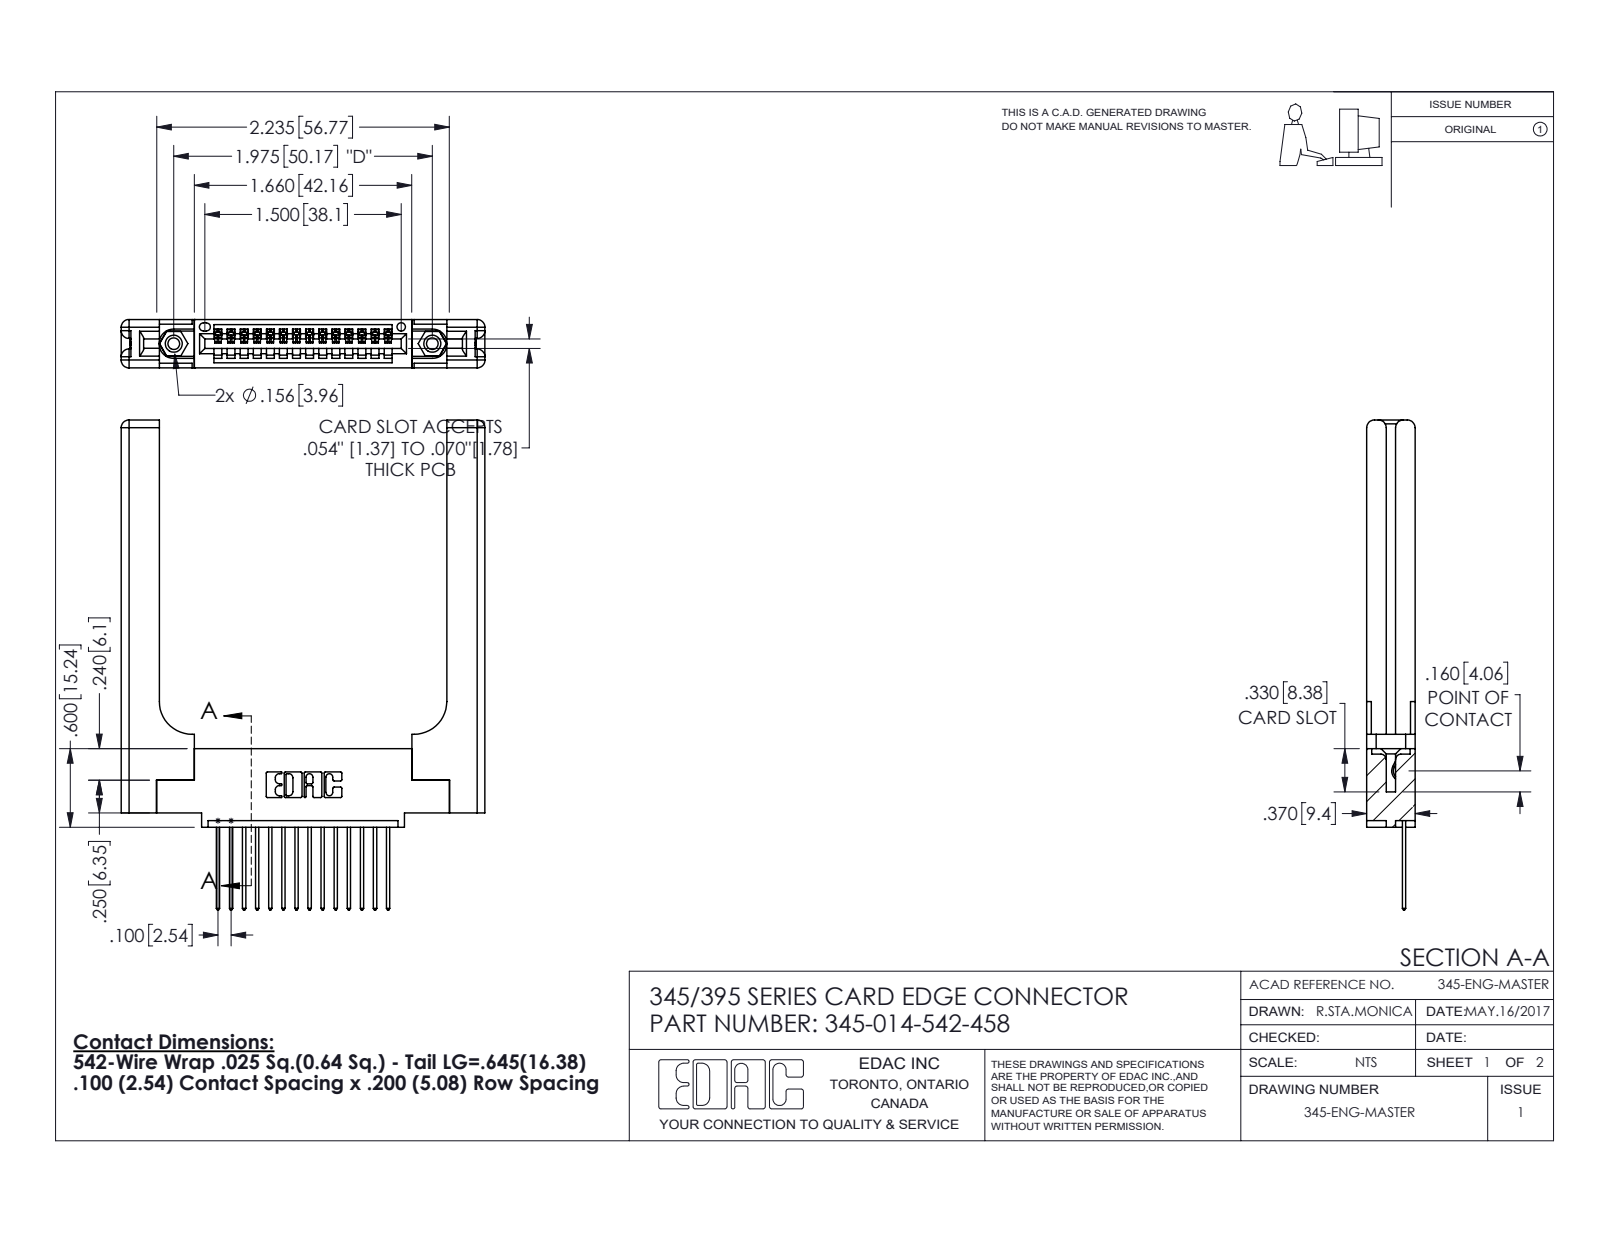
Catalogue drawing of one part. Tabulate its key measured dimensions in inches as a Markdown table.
| quantity | value |
| --- | --- |
| part name | 345-014-542-458; 345-220-058_345-220-058; 345-250-001_345-250-001-102; 345-292-001_345-293-142 (+1 more) |
| STEP written by | SolidWorks 2016 (CONFIG_CONTROL_DESIGN) |
| units | inches |
| bodies | 19 solids, 1198 faces (792 planar, 346 cylindrical, 60 other) |
| overall size | 3.742 × 2.779 × 0.37 |
| volume | 0.912 in³ |
| surface area | 21.32 in² |
| round holes (diameter × count) | 0.089 × 2, 0.125 × 2, 0.156 × 2, 0.064 × 1 |
| round bosses / shafts (diameter × count) | 0.155 × 2 |
| partial cylindrical surfaces (radius × count) | 0.006 × 28, 0.01 × 28, 0.01 × 22, 0.06 × 16, 0.007 × 6, 0.031 × 6, 0.026 × 3, 0.03 × 2 |
| main face-to-face distances | 0.37, 0.072, 0.298, 0.15, 0.148, 0.077, 0.22, 0.2, 0.098, 0.272 |
| hole center spacings | 0.27, 1.742, 1.975 |
